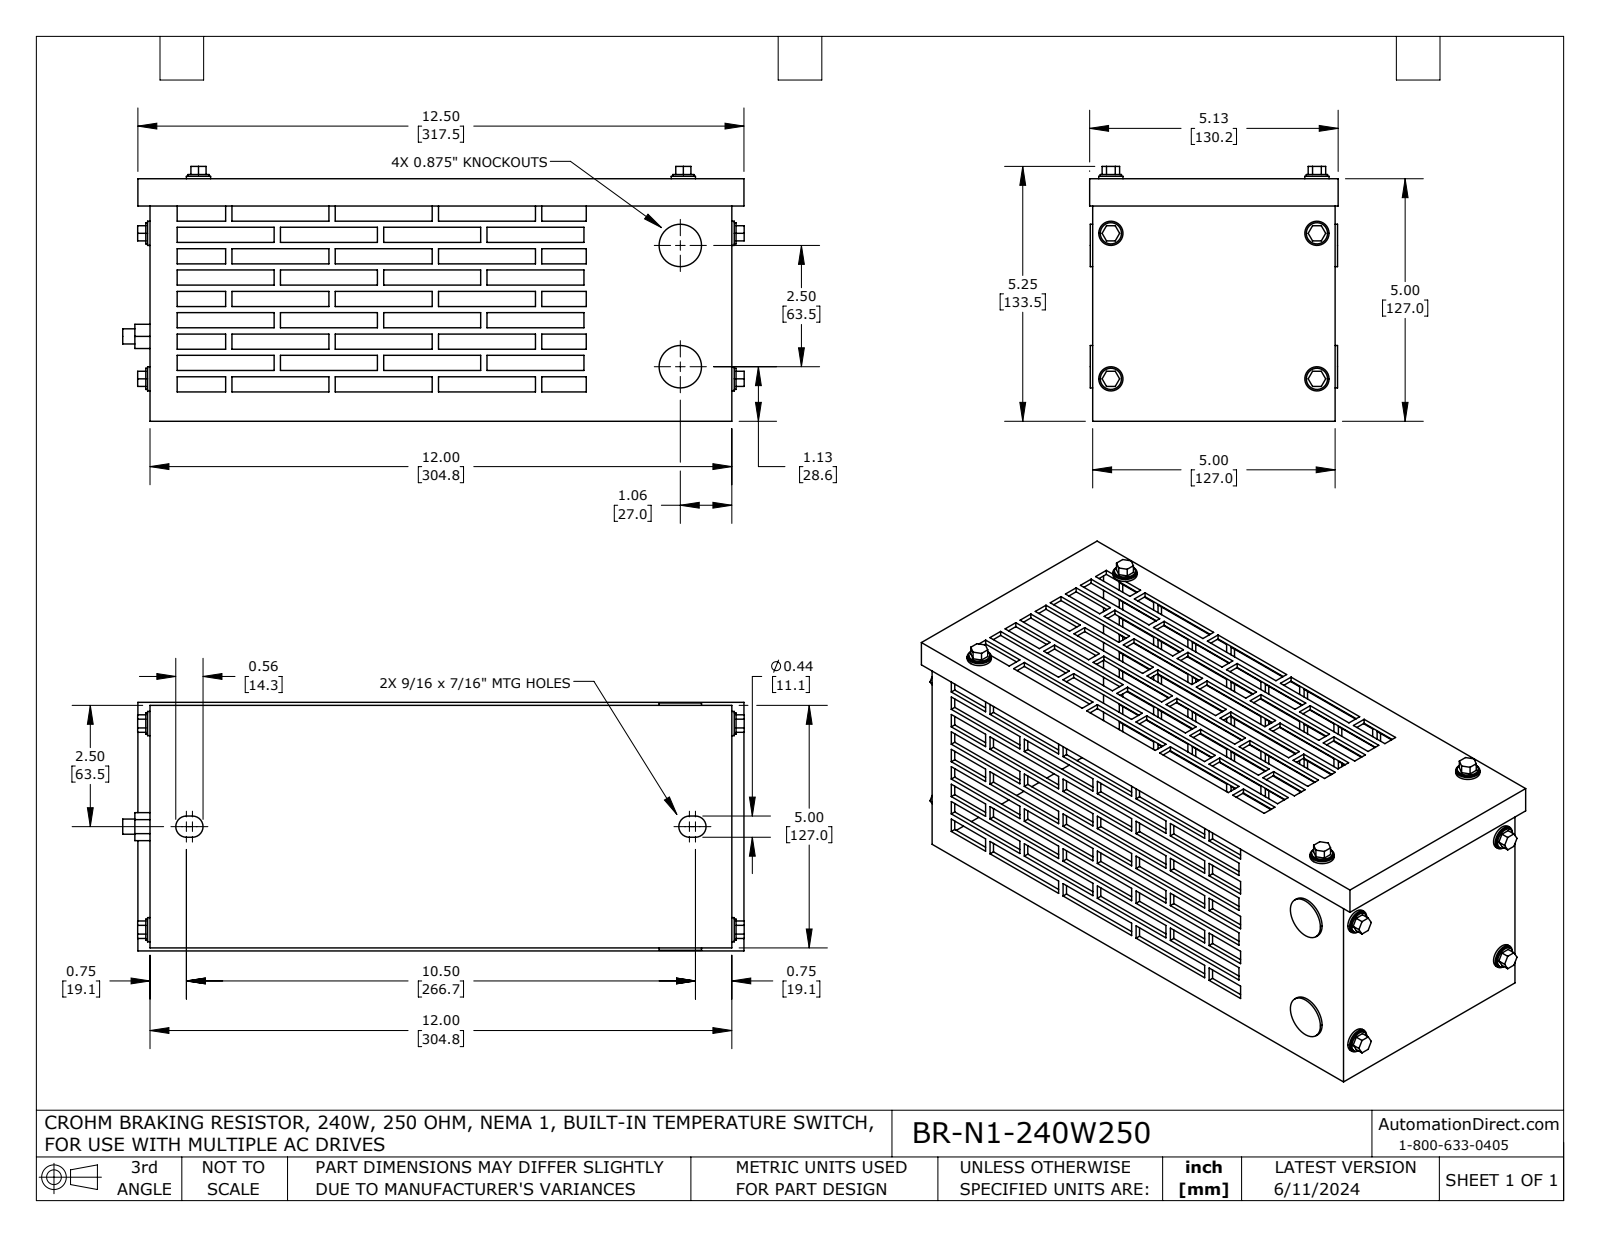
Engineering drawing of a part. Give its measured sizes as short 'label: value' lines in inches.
name: BR-N1-240W250
written by: SolidWorks 2021 (AUTOMOTIVE_DESIGN)
unit: in
bodies: 30 solids, 753 faces (659 planar, 94 cylindrical, 0 other)
size: 12.817 × 5.254 × 5.125
volume: 22.6 in³; area: 511.7 in²
holes: 8× ⌀0.25, 2× ⌀0.75
bosses: 8× ⌀0.5, 8× ⌀0.437, 2× ⌀0.875, 1× ⌀0.313
rounds: 4× R0.219
face distances: 0.1, 4.9, 5, 4.8, 11.9, 0.063, 4.963, 12, 11.8, 0.88
hole spacings: 4.25, 3, 5.202, 10, 10.865, 2.5
